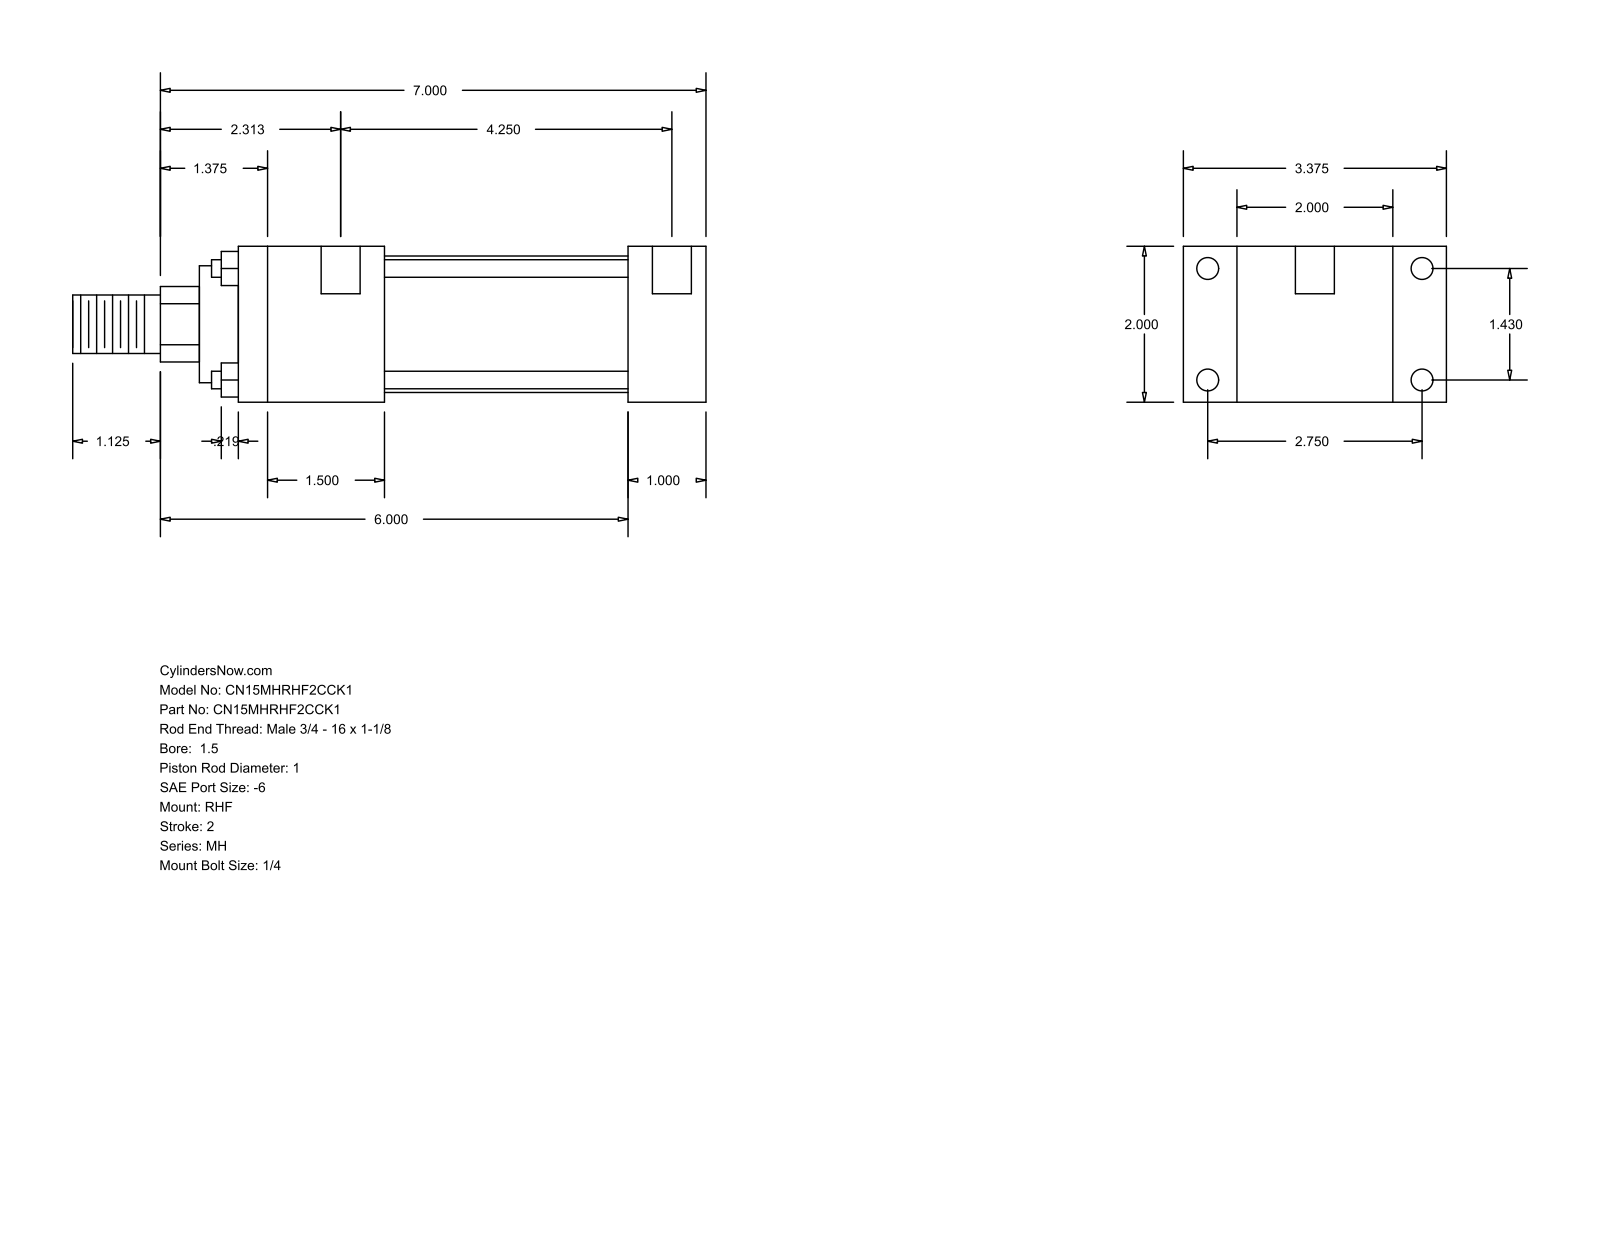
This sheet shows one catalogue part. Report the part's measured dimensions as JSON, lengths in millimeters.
{"part_name": "MH_RHF__0150_1", "step_written_by": "GSSL Pune (CONFIG_CONTROL_DESIGN)", "units": "millimeters", "bodies": {"solids": 0, "faces": 88, "planar": 60, "cylindrical": 28, "other": 0}, "overall_size": [206.38, 85.72, 50.8], "round_holes": [[5.56, 4], [7.14, 4], [12.7, 2]], "round_bosses_or_shafts": [[5.71, 4], [44.45, 1], [38.1, 1], [25.4, 1], [19.05, 1]], "partial_cylinders_radius": [[12.29, 1]], "face_to_face_distances": [50.8, 25.4, 17.46, 68.26, 85.72, 152.4, 127, 47.63, 79.37, 104.77], "hole_center_spacings": [36.32, 69.84, 78.72, 111.13, 3.18, 107.95]}
